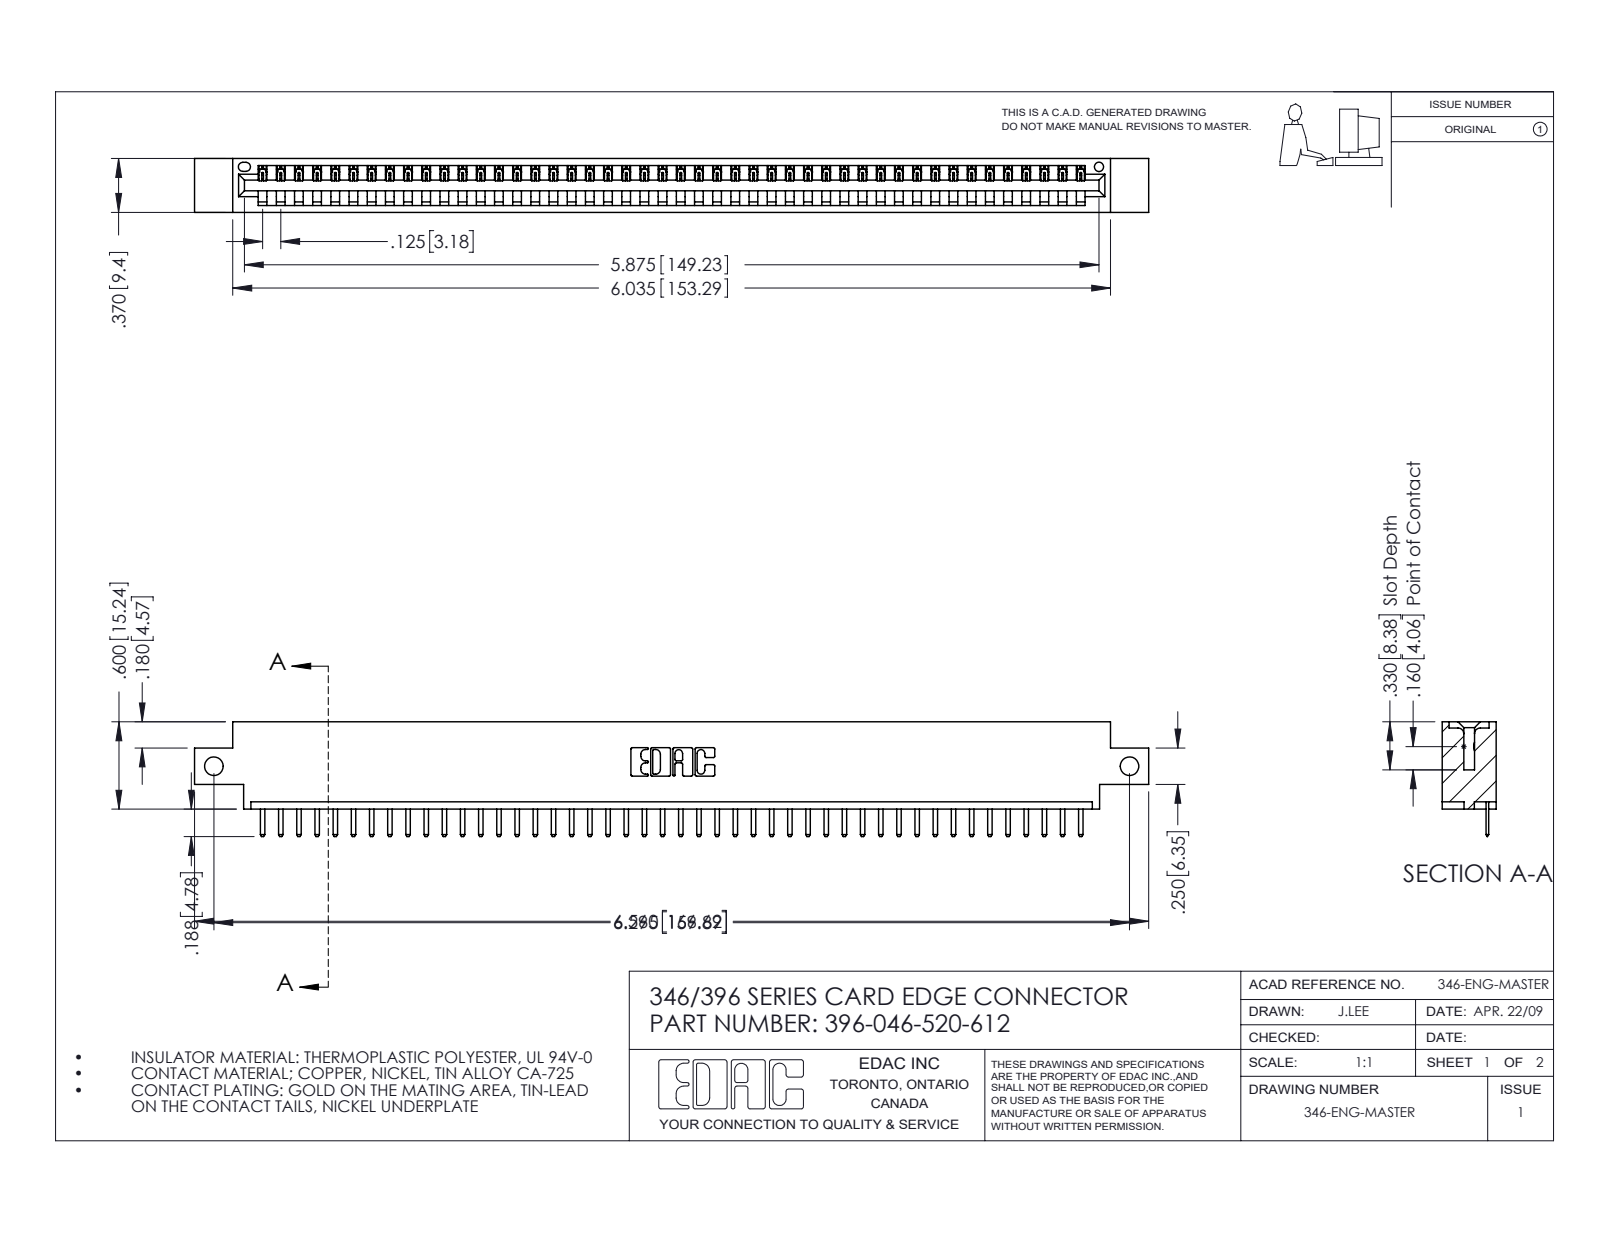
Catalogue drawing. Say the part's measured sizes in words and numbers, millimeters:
The part is named "346 Part_0.170 Offset - Side Mount; 396-046-520-612; 345-292-001_345-293-120". Its 3-D file was written by "SolidWorks 2016 (CONFIG_CONTROL_DESIGN)". It is 47 solids with 2978 faces: 2012 planar, 966 cylindrical and 0 other. Overall it measures 166.6 by 20 by 9.4 millimeters. Its volume is 15 600 cubic millimeters and its surface area 19 120 square millimeters. Round holes: 2 of diameter 3.3, 1 of diameter 1.6. Partial cylindrical surfaces (rounded edges, fillets, slot ends): 94 of radius 0.3, 92 of radius 0.2, 22 of radius 0.3, 6 of radius 0.2, 6 of radius 0.8, 3 of radius 0.7, 2 of radius 0.8, 2 of radius 1. The main face-to-face distances are 1.2, 8.2, 9.4, 6.4, 3.8, 5.6, 2.5, 4.4, 1.8, 7.6. The hole center spacings are 159.9.
